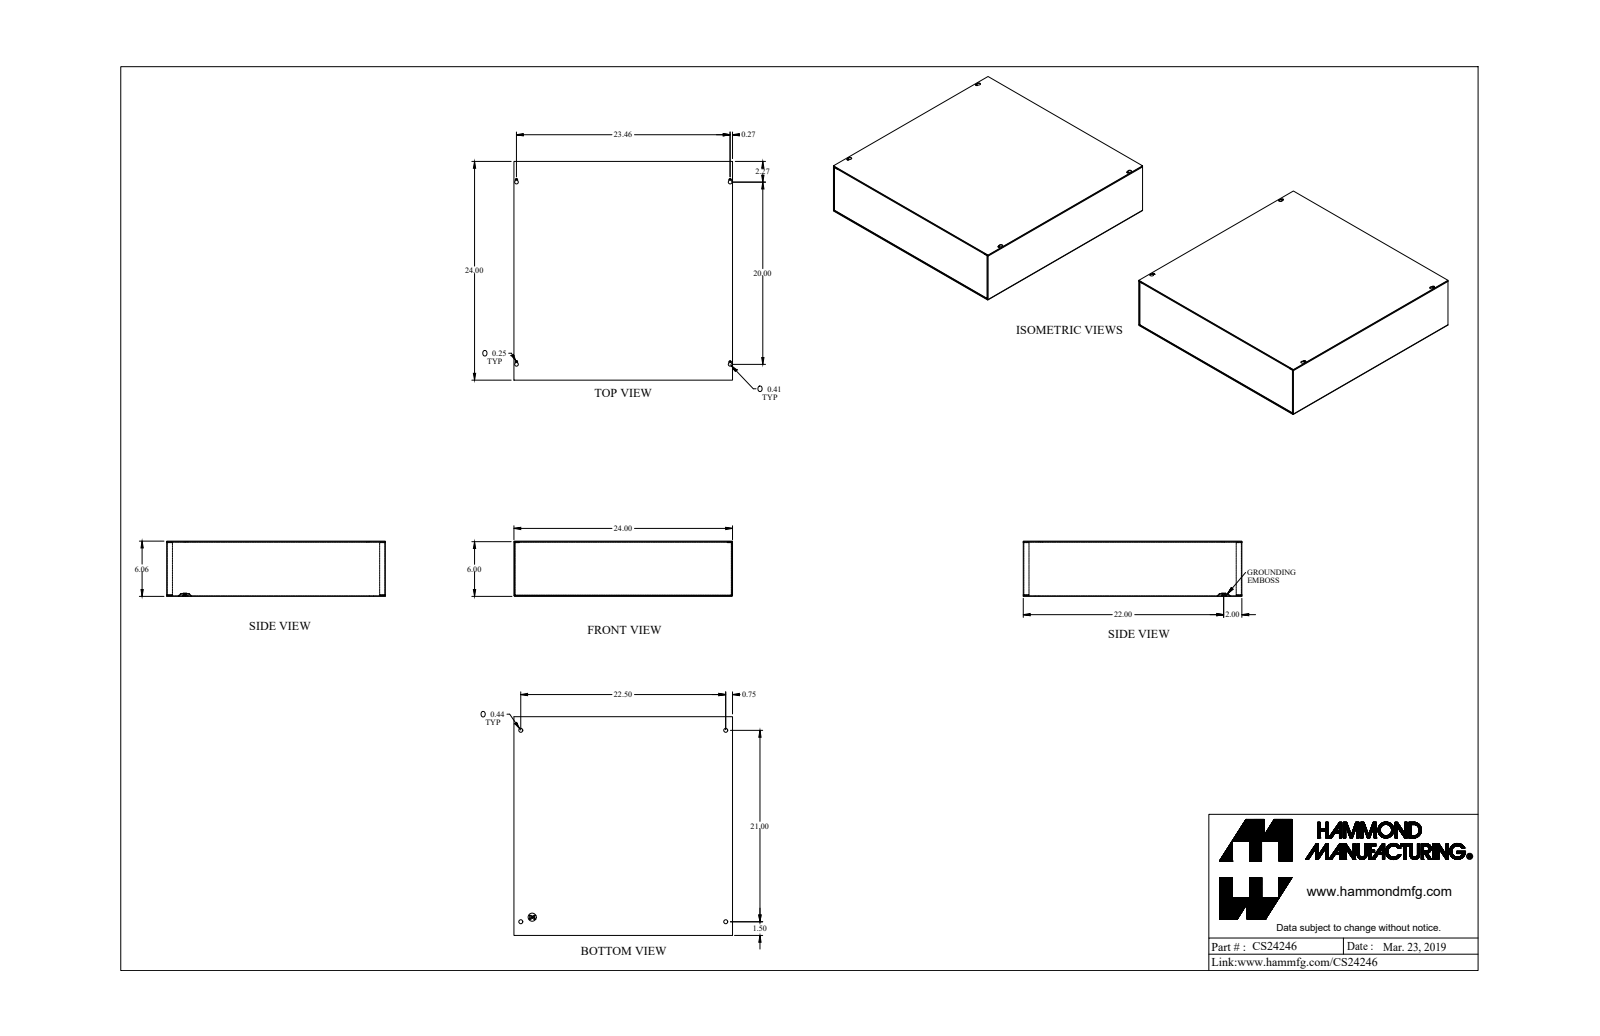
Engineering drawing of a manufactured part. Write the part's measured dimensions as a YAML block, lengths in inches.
part_name: "CS24246_Default"
step_written_by: "SolidWorks 2019 (CONFIG_CONTROL_DESIGN)"
units: inches
bodies: {solids: 4, faces: 205, planar: 125, cylindrical: 72, other: 8}
overall_size: [24, 24, 6.057]
volume: 102.3
surface_area: 3610
round_holes:
  - {diameter: 0.17, count: 5}
  - {diameter: 0.437, count: 4}
  - {diameter: 0.5, count: 1}
round_bosses_or_shafts:
  - {diameter: 0.492, count: 1}
  - {diameter: 0.284, count: 1}
partial_cylinders:
  - {radius: 0.029, count: 12}
  - {radius: 0.086, count: 12}
  - {radius: 0.057, count: 8}
  - {radius: 0.125, count: 4}
  - {radius: 0.203, count: 4}
face_to_face_distances: [0.057, 6, 5.943, 6.057, 23.943, 24, 23.886, 0.08, 5.863, 5.92]
hole_center_spacings: [0.693, 20.506, 22.985, 30.795, 20, 21, 22.5, 23.46]
